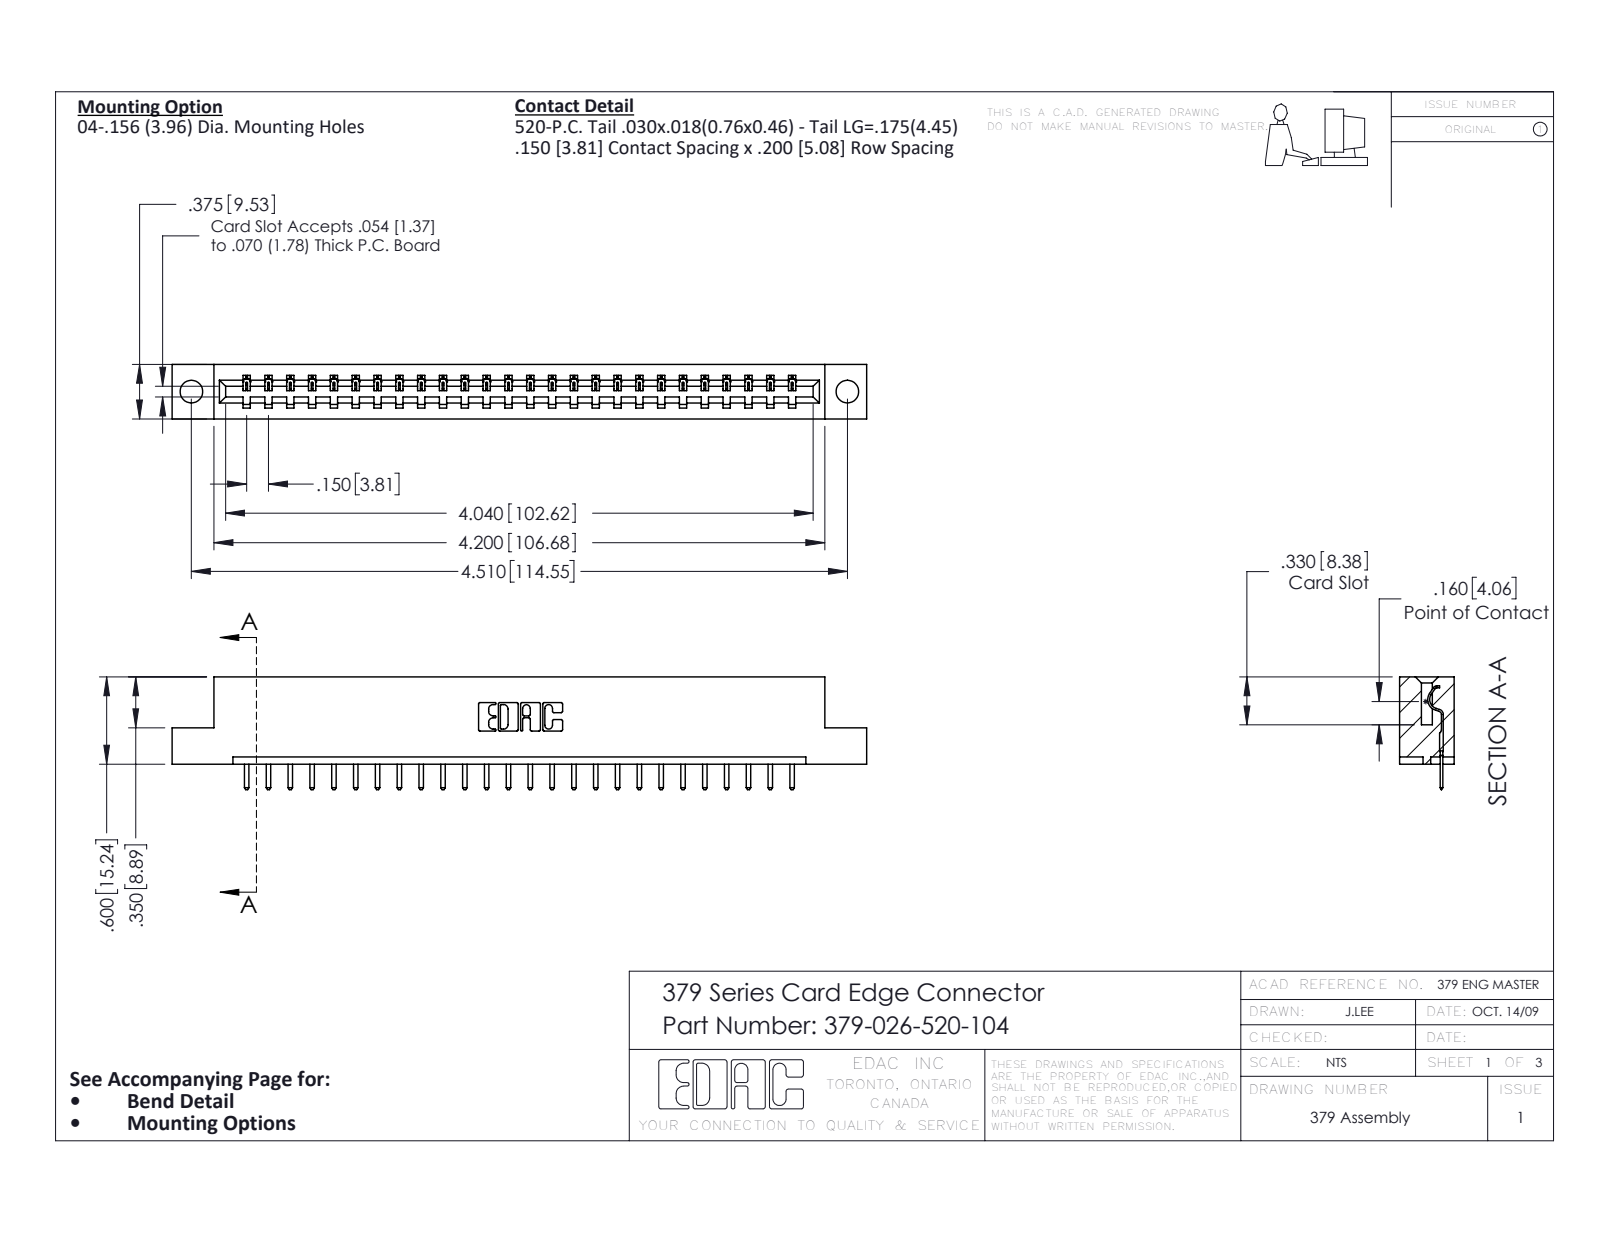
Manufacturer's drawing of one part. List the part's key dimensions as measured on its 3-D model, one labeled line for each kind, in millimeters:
Part name (STEP PRODUCT): 379-026-520-104; 345-292-001_345-293-120; 379 Part_Flush - .156 Dia - TH
STEP written by: SolidWorks 2016 (CONFIG_CONTROL_DESIGN)
Units: millimetres
Bodies: 27 solids, 1726 faces (1214 planar, 512 cylindrical, 0 other)
Overall size (bounding box): 121.3 × 19.7 × 9.5
Volume: 12 400 mm³ · Surface area: 12 120 mm²
Round holes (diameter × count): ⌀4 ×2
Partial cylindrical surfaces — rounded edges, fillets, slot ends (radius × count): R0.3 ×54, R0.2 ×52, R0.3 ×22, R0.2 ×6, R0.8 ×6, R0.7 ×3, R0.4 ×1, R0.6 ×1
Main face-to-face distances: 7.6, 1.9, 9.5, 5.7, 15.2, 3.8, 5.1, 14, 11.4, 3.8
Hole centre spacings: 114.6
